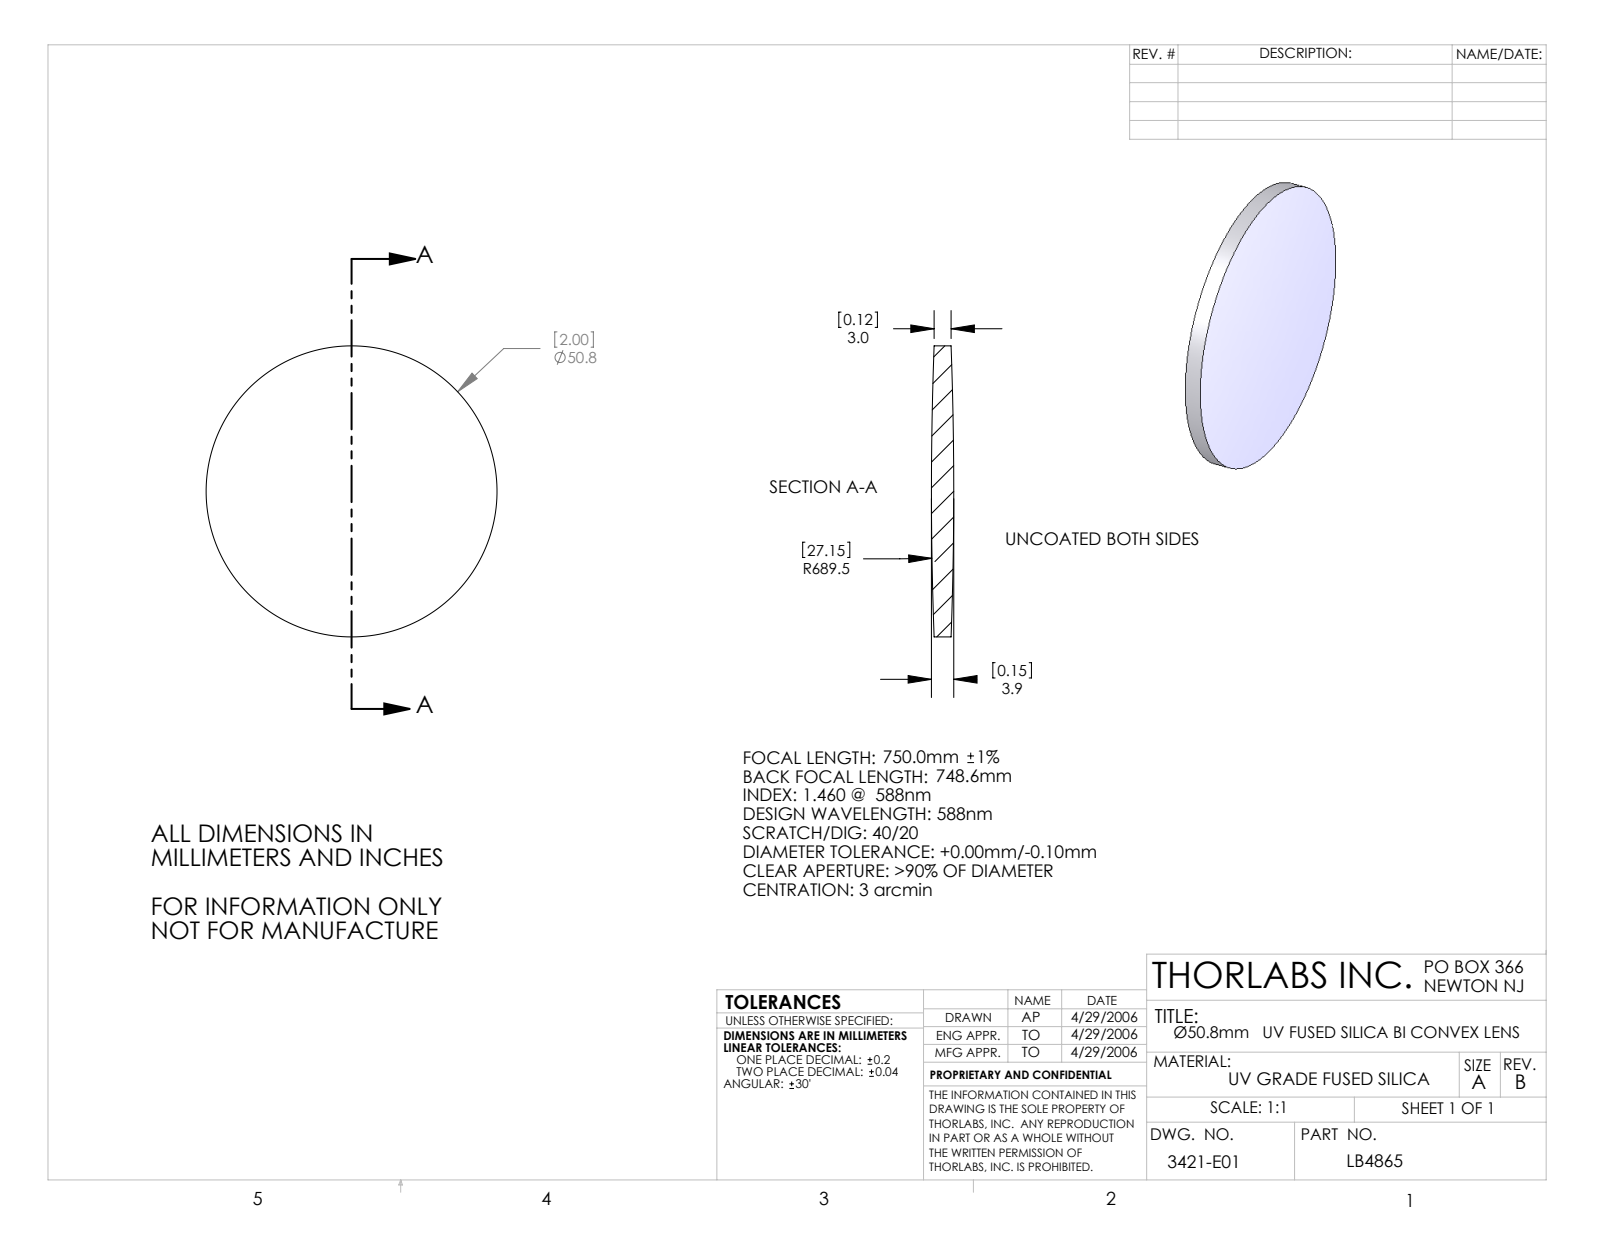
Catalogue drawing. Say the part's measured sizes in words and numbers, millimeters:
The part is named "3421-E0W". Its 3-D file was written by "SolidWorks 2007 (AUTOMOTIVE_DESIGN)". It is 1 solid with 6 faces: 0 planar, 2 cylindrical and 4 other. Overall it measures 50.8 by 50.8 by 3.9 millimeters. Its volume is 6 950 cubic millimeters and its surface area 4 528 square millimeters. Round bosses or shafts: 1 of diameter 50.8.
